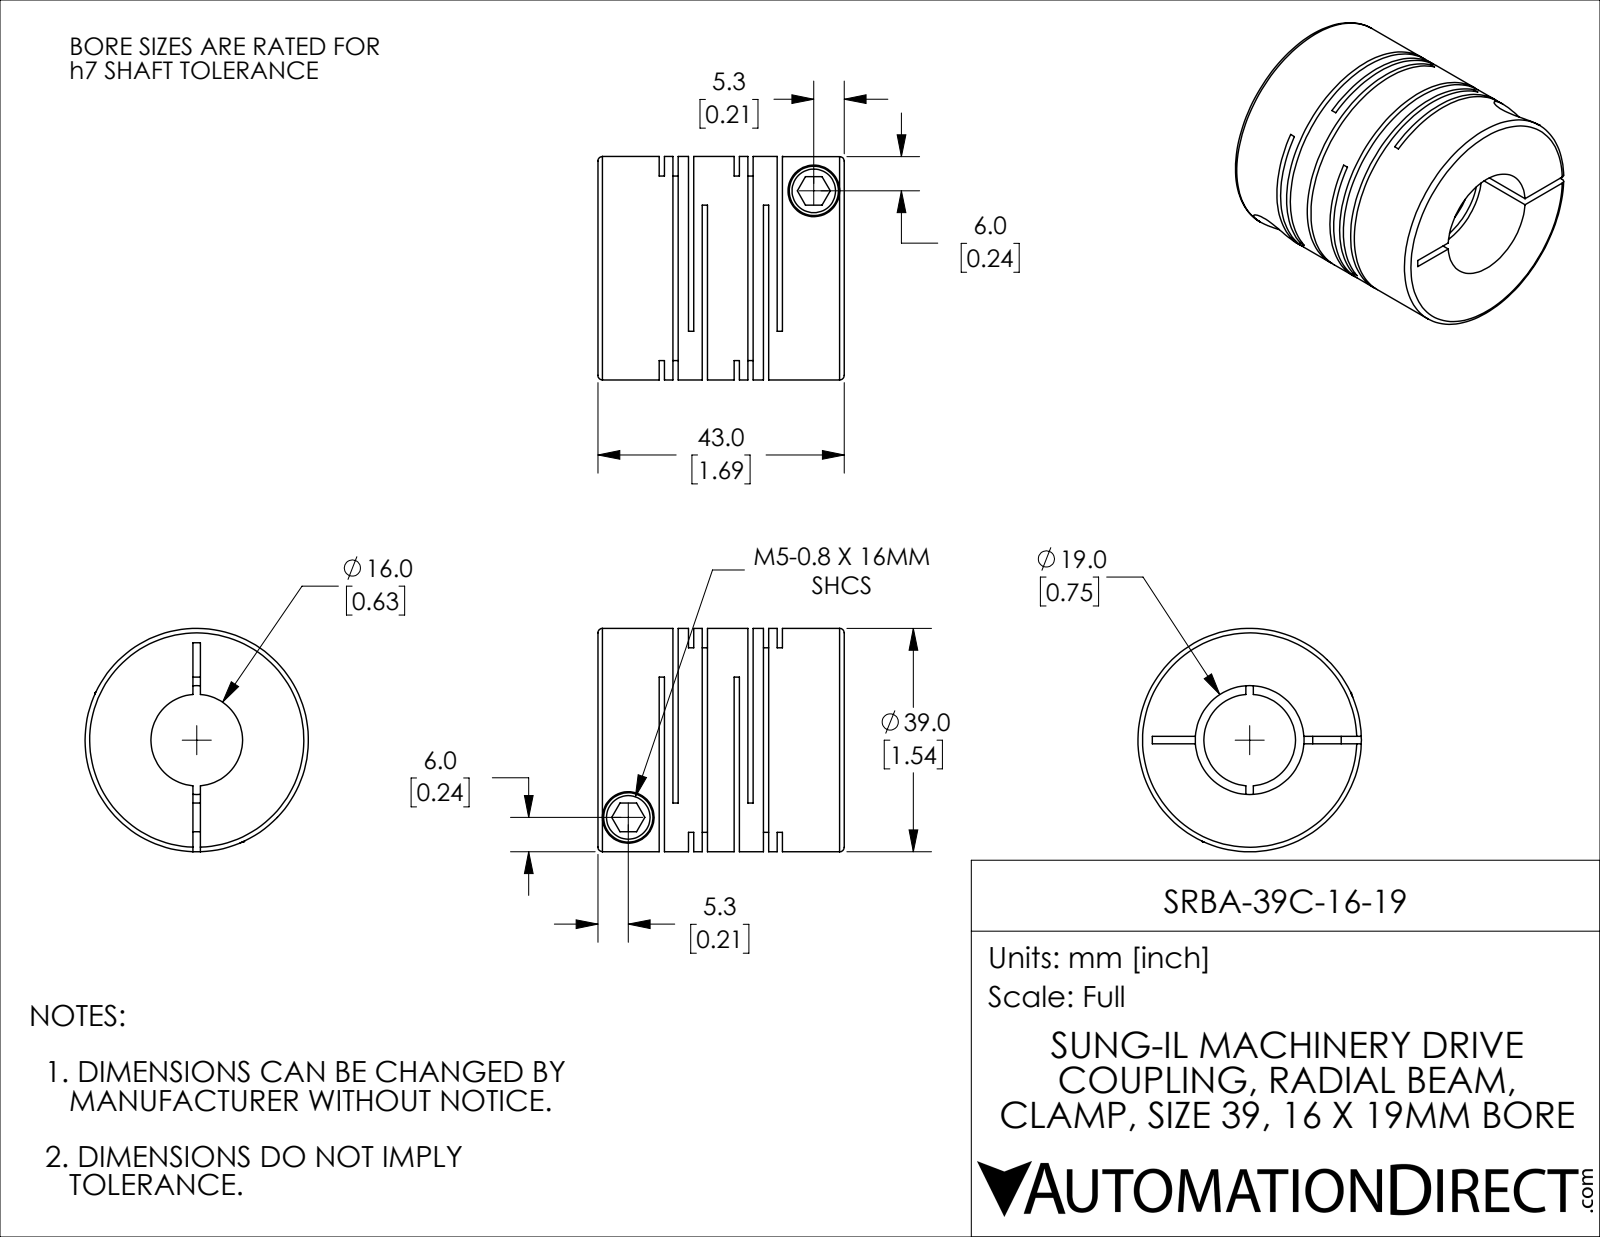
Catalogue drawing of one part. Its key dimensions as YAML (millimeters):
part_name: "SRBA-39C-16-19"
step_written_by: "SolidWorks 2021 (CONFIG_CONTROL_DESIGN)"
units: millimeters
bodies: {solids: 1, faces: 114, planar: 60, cylindrical: 42, other: 12}
overall_size: [43, 39, 39]
volume: 33328
surface_area: 21795
round_holes:
  - {diameter: 5, count: 2}
  - {diameter: 9, count: 2}
  - {diameter: 16, count: 1}
  - {diameter: 19, count: 1}
round_bosses_or_shafts:
  - {diameter: 8.6, count: 2}
  - {diameter: 39, count: 1}
face_to_face_distances: [13.1, 0.92, 2.4, 5.1, 10.7, 14.02, 18.2, 3.32, 15.5, 1.48]
